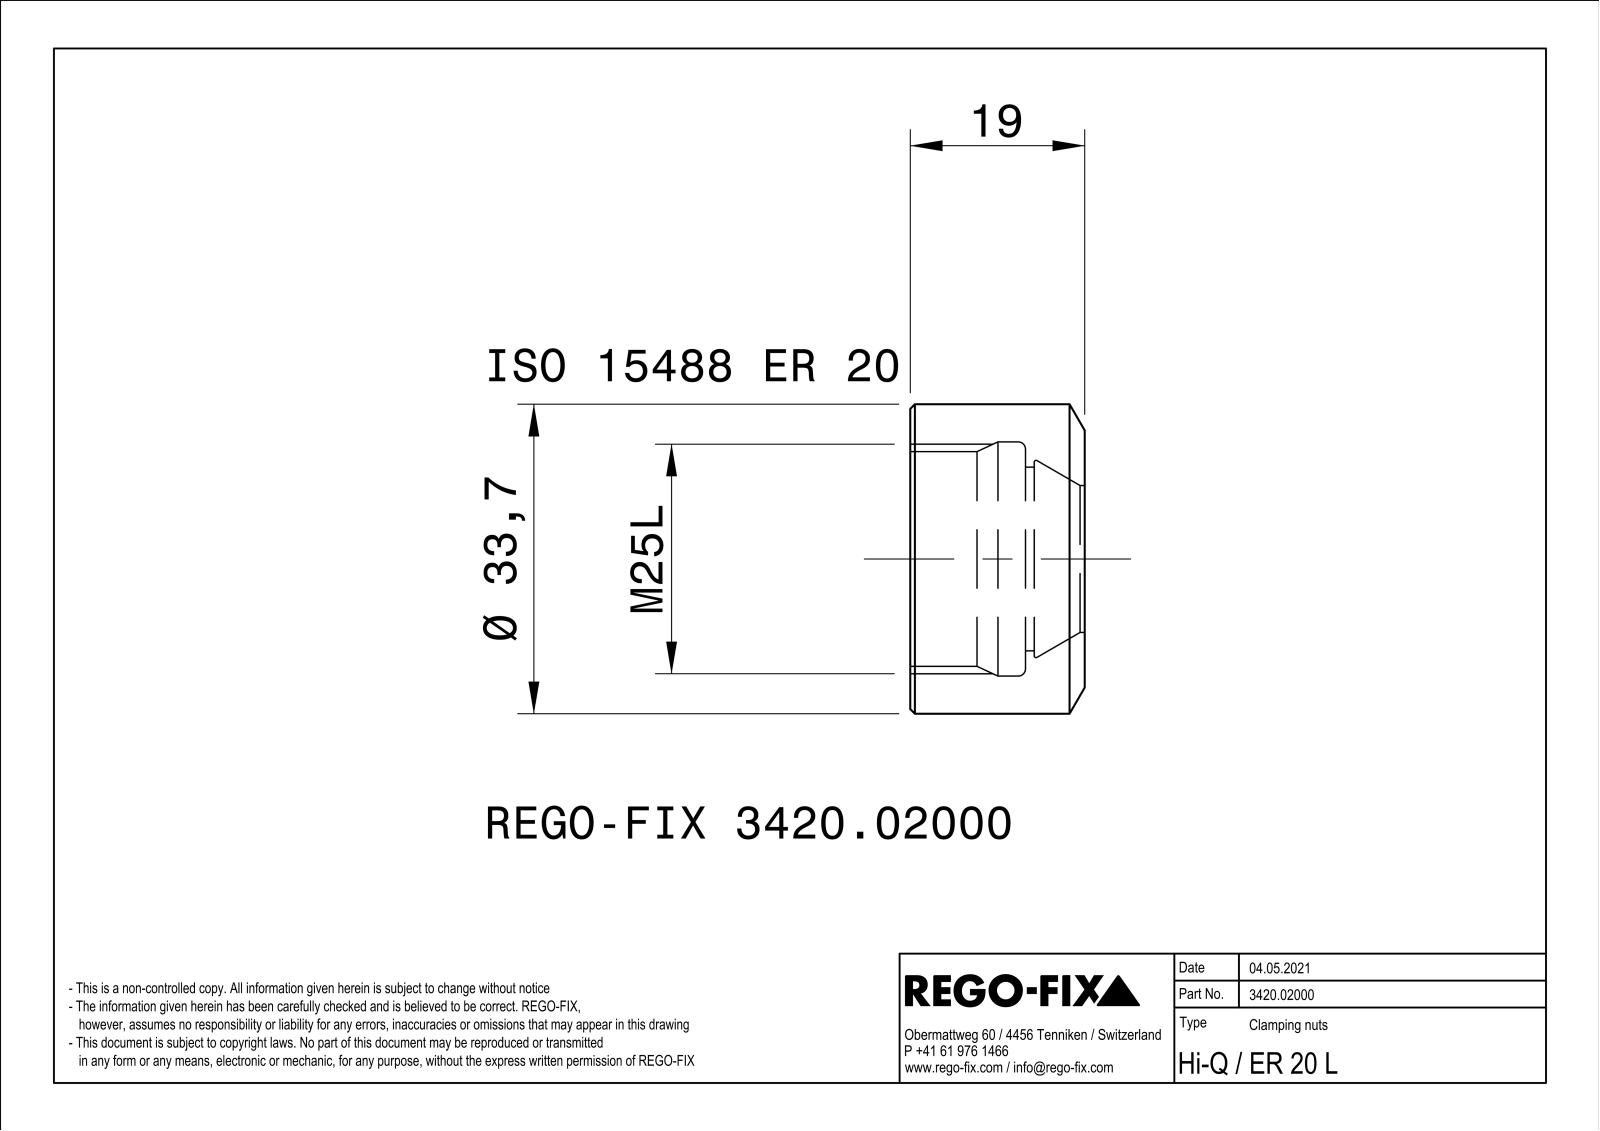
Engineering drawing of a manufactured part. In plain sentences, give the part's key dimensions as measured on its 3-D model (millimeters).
The part is named "NOCUT". Its 3-D file was written by "SIEMENS PLM Software Solid Edge ST10 (AUTOMOTIVE_DESIGN)". It is 1 solid with 27 faces: 16 planar, 5 cylindrical and 6 other. Overall it measures 33.7 by 33.7 by 19 millimeters. Its volume is 7 972 cubic millimeters and its surface area 4 549 square millimeters. Round holes: 1 of diameter 16, 1 of diameter 20, 1 of diameter 23.38, 1 of diameter 25.5. Round bosses or shafts: 1 of diameter 33.7. The main face-to-face distances are 30, 19, 6.45, 12.55, 5.5, 0.95, 13.5.
